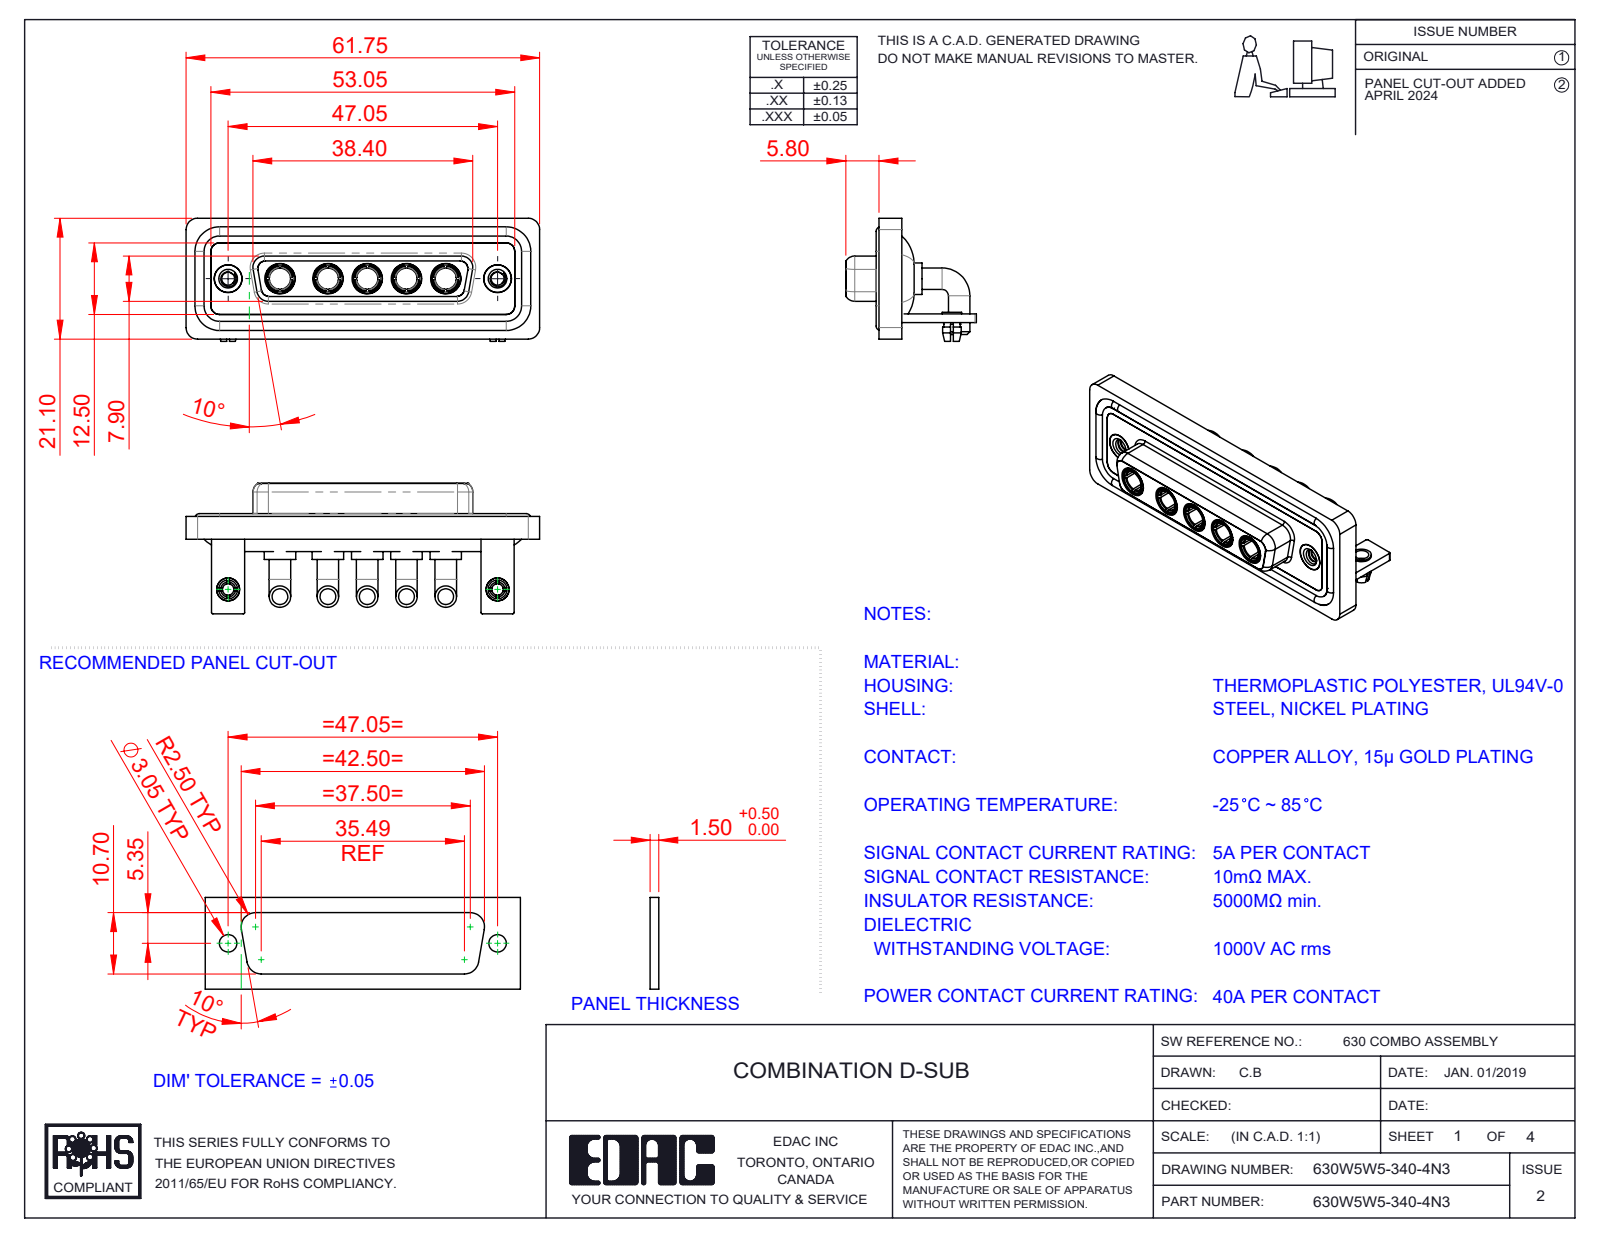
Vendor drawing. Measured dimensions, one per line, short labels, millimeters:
name: Power Socket_40A RA; 630Combo Waterproof Housing_25 Contacts; 630Combo Board Lock_50 Contacts; 630Combo Shell Front_25 Contacts (+5 more)
written by: SolidWorks 2023 (CONFIG_CONTROL_DESIGN)
unit: mm
bodies: 21 solids, 916 faces (318 planar, 369 cylindrical, 229 other)
size: 61.75 × 22.8 × 21.5
volume: 9 201 mm³; area: 14 978 mm²
holes: 7× ⌀4.85, 5× ⌀3.7, 5× ⌀5.3, 2× ⌀2, 2× ⌀2.26, 2× ⌀2.5, 2× ⌀3.2, 2× ⌀4, 2× ⌀4.05, 2× ⌀5
bosses: 10× ⌀3.75, 5× ⌀5.5, 5× ⌀5.2, 5× ⌀4.96, 5× ⌀4.75, 4× ⌀1.6, 2× ⌀4.95, 2× ⌀4.8
rounds: 19× R2, 18× R1.5, 16× R0.25, 8× R1.35, 8× R1.6, 5× R0.5, 5× R2.1, 4× R0.6
face distances: 0.4, 1.8, 2.9, 3.7, 1.5, 4.1, 1.1, 1.4, 1.6, 2.5
hole spacings: 6.86, 9.04, 38.01, 47.05, 6.87, 8.38, 13.72, 13.73
